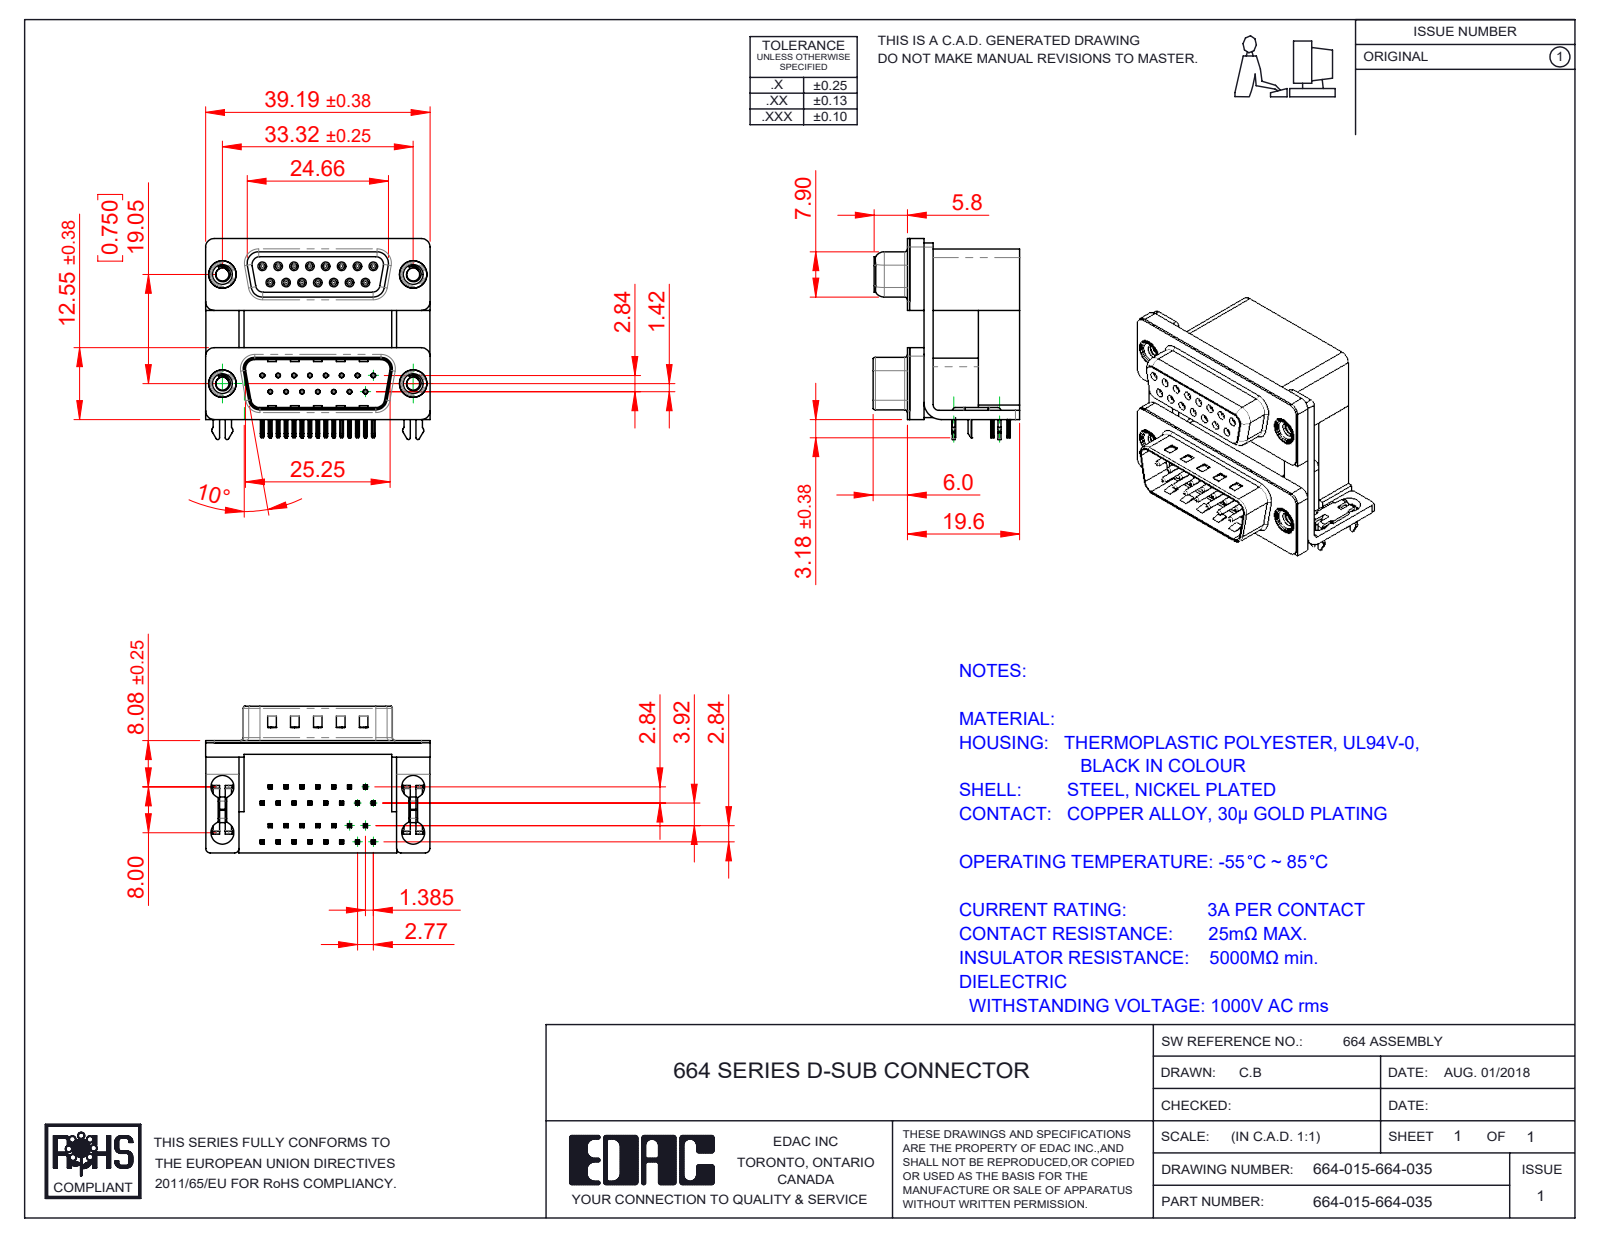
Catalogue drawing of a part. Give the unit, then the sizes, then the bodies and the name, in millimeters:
Units: millimetres
Overall size (bounding box): 39.19 × 35.1 × 25.6
Round holes (diameter × count): ⌀0.8 ×30, ⌀0.35 ×15, ⌀0.9 ×15, ⌀4 ×8, ⌀2.26 ×4, ⌀3.5 ×4, ⌀4.8 ×4, ⌀5 ×4
Round bosses / shafts (diameter × count): ⌀1.2 ×15, ⌀0.75 ×15, ⌀4.9 ×4, ⌀4.75 ×4, ⌀3.9 ×4
Partial cylindrical surfaces — rounded edges, fillets, slot ends (radius × count): R0.1 ×122, R0.25 ×70, R0.15 ×60, R0.12 ×30, R0.35 ×30, R0.5 ×16, R1.5 ×16, R0.34 ×15
Main face-to-face distances: 0.4, 19.2, 16.7, 2.5, 7.2, 12, 9.5, 10.69, 2.19, 2.9
Hole centre spacings: 3.16, 2.77, 19.25, 5.54, 19.84, 8.31, 19.05, 20.78
Volume: 15 183 mm³ · Surface area: 17 094 mm²
Bodies: 43 solids, 4064 faces (2117 planar, 1064 cylindrical, 883 other)
Part name (STEP PRODUCT): 664 Contact Bottom Upper_M; 664 Housing Upper_15 Contacts M; 664 Shell Receptacle_15 Contacts; 664 2 Prong Board Lock_3 (+8 more)
STEP written by: SolidWorks 2020 (CONFIG_CONTROL_DESIGN)
